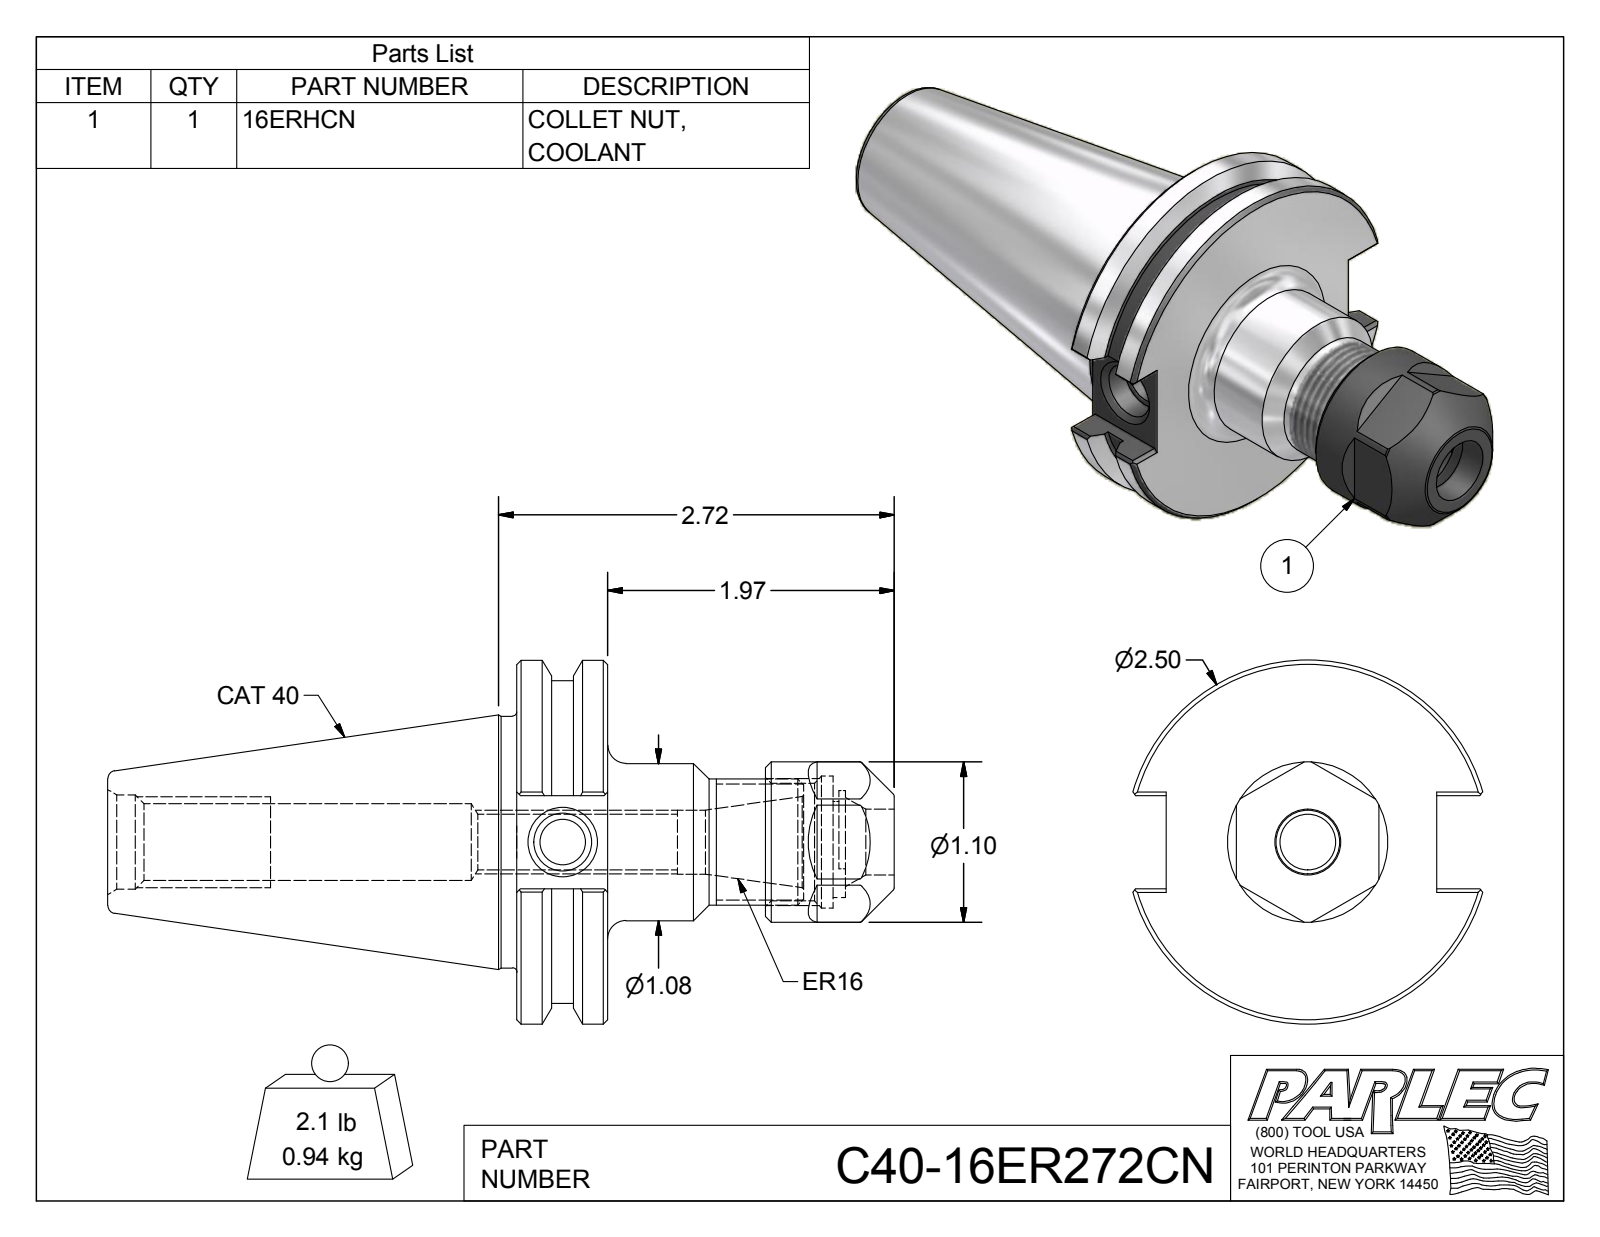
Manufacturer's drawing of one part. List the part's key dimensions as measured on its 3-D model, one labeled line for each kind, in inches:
Part name (STEP PRODUCT): C40-16ER272CN; C40-16ER262-1; 16ERHCN
STEP written by: Autodesk Inventor 2012 (AUTOMOTIVE_DESIGN)
Units: inches
Bodies: 2 solids, 104 faces (49 planar, 21 cylindrical, 34 other)
Overall size (bounding box): 5.408 × 2.5 × 2.403
Volume: 7.364 in³ · Surface area: 42.61 in²
Round holes (diameter × count): ⌀0.315 ×1, ⌀0.383 ×1, ⌀0.396 ×1, ⌀0.44 ×1, ⌀0.453 ×1, ⌀0.527 ×1, ⌀0.648 ×1, ⌀0.661 ×1, ⌀0.807 ×1, ⌀0.906 ×1
Round bosses / shafts (diameter × count): ⌀2.5 ×1, ⌀2.219 ×1, ⌀1.73 ×1, ⌀1.102 ×1, ⌀1.08 ×1, ⌀0.866 ×1
Partial cylindrical surfaces — rounded edges, fillets, slot ends (radius × count): R0.354 ×1
Main face-to-face distances: 0.625, 0.979, 2.174, 1.549, 0.64, 1.86, 1.709, 1.084, 0.465, 2.812
Hole centre spacings: 0.051
